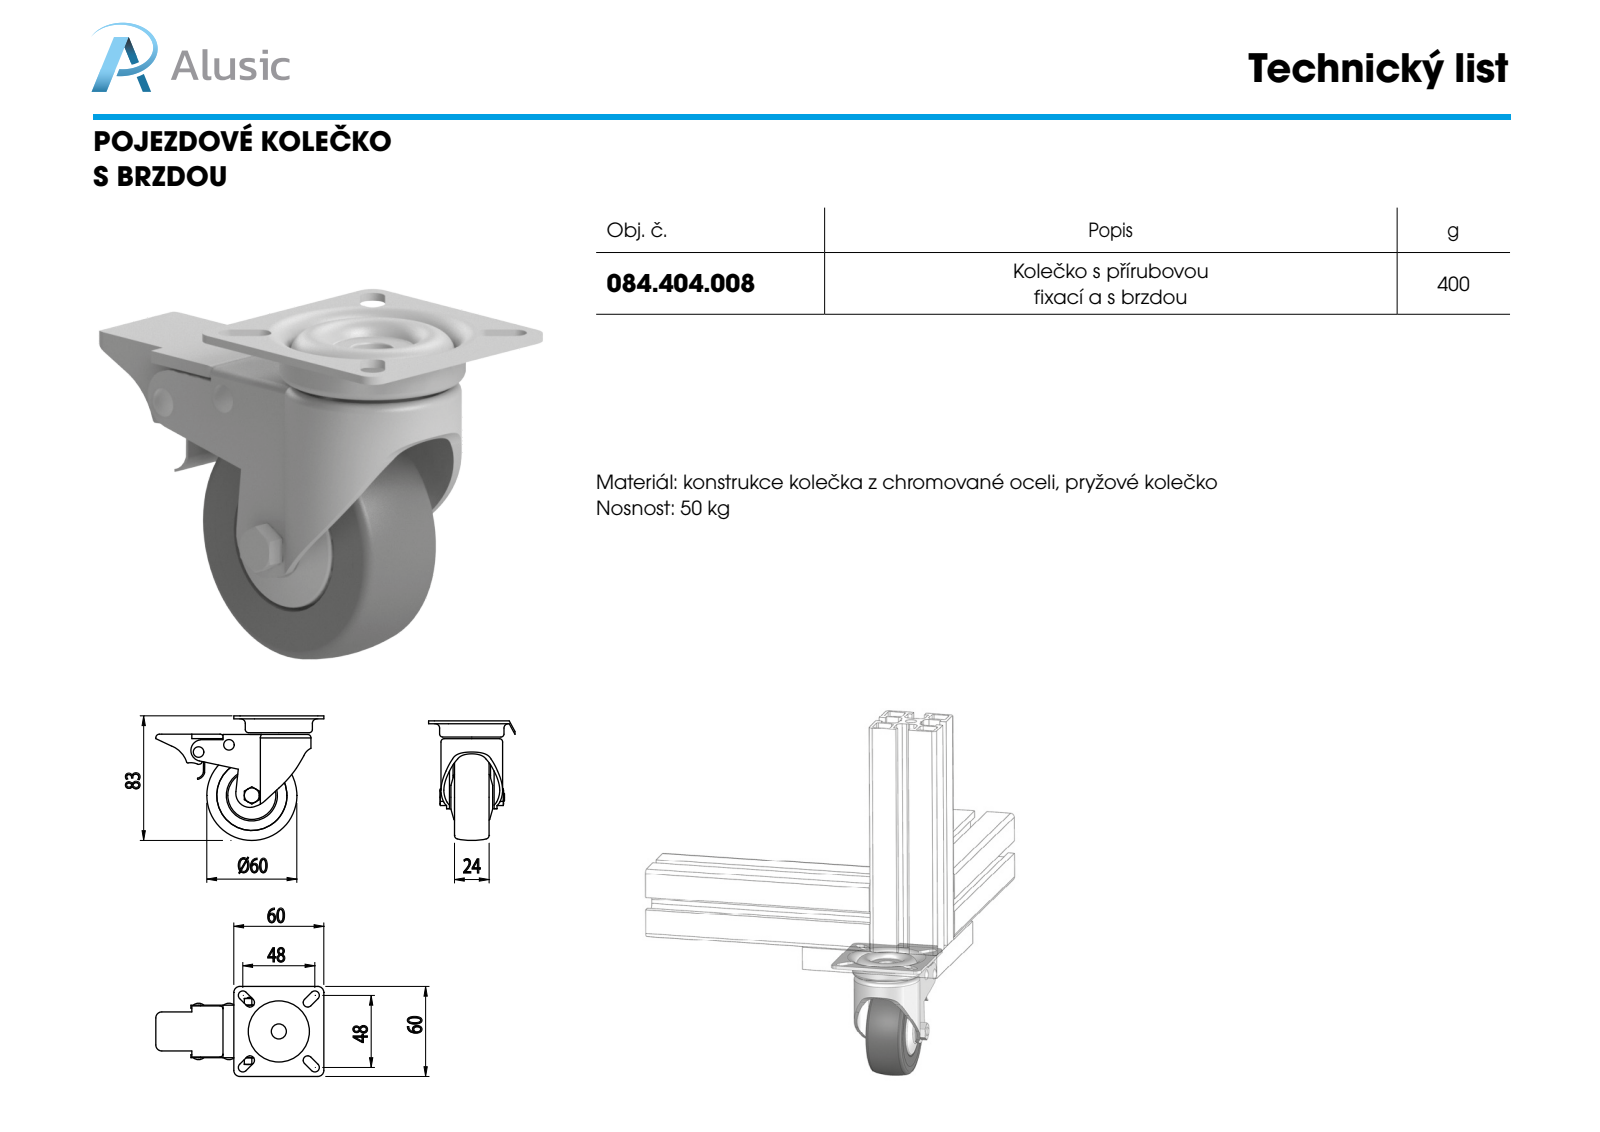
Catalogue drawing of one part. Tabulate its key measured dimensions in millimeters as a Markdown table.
| quantity | value |
| --- | --- |
| part name | 084.404.008 |
| STEP written by | SolidWorks 2011 (CONFIG_CONTROL_DESIGN) |
| units | millimeters |
| bodies | 8 solids, 336 faces (99 planar, 120 cylindrical, 117 other) |
| overall size | 112 × 83 × 60 |
| volume | 108 123 mm³ |
| surface area | 49 352 mm² |
| round holes (diameter × count) | 4.92 × 1, 6 × 1, 8 × 1, 10.02 × 1, 31 × 1, 34 × 1, 34 × 1, 38.8 × 1, 40.72 × 1, 46.74 × 1 |
| round bosses / shafts (diameter × count) | 4 × 2, 46.7 × 1, 44.72 × 1, 39.72 × 1, 32 × 1, 31.72 × 1, 28 × 1, 7.9 × 1 |
| partial cylindrical surfaces (radius × count) | 3 × 8, 4 × 6, 2 × 5, 0.5 × 2, 0.89 × 1, 1.61 × 1, 1.61 × 1, 2.31 × 1 |
| main face-to-face distances | 2, 3.5, 29.5, 27.5, 1, 5.5, 33, 2.5, 1.5, 28.5 |
